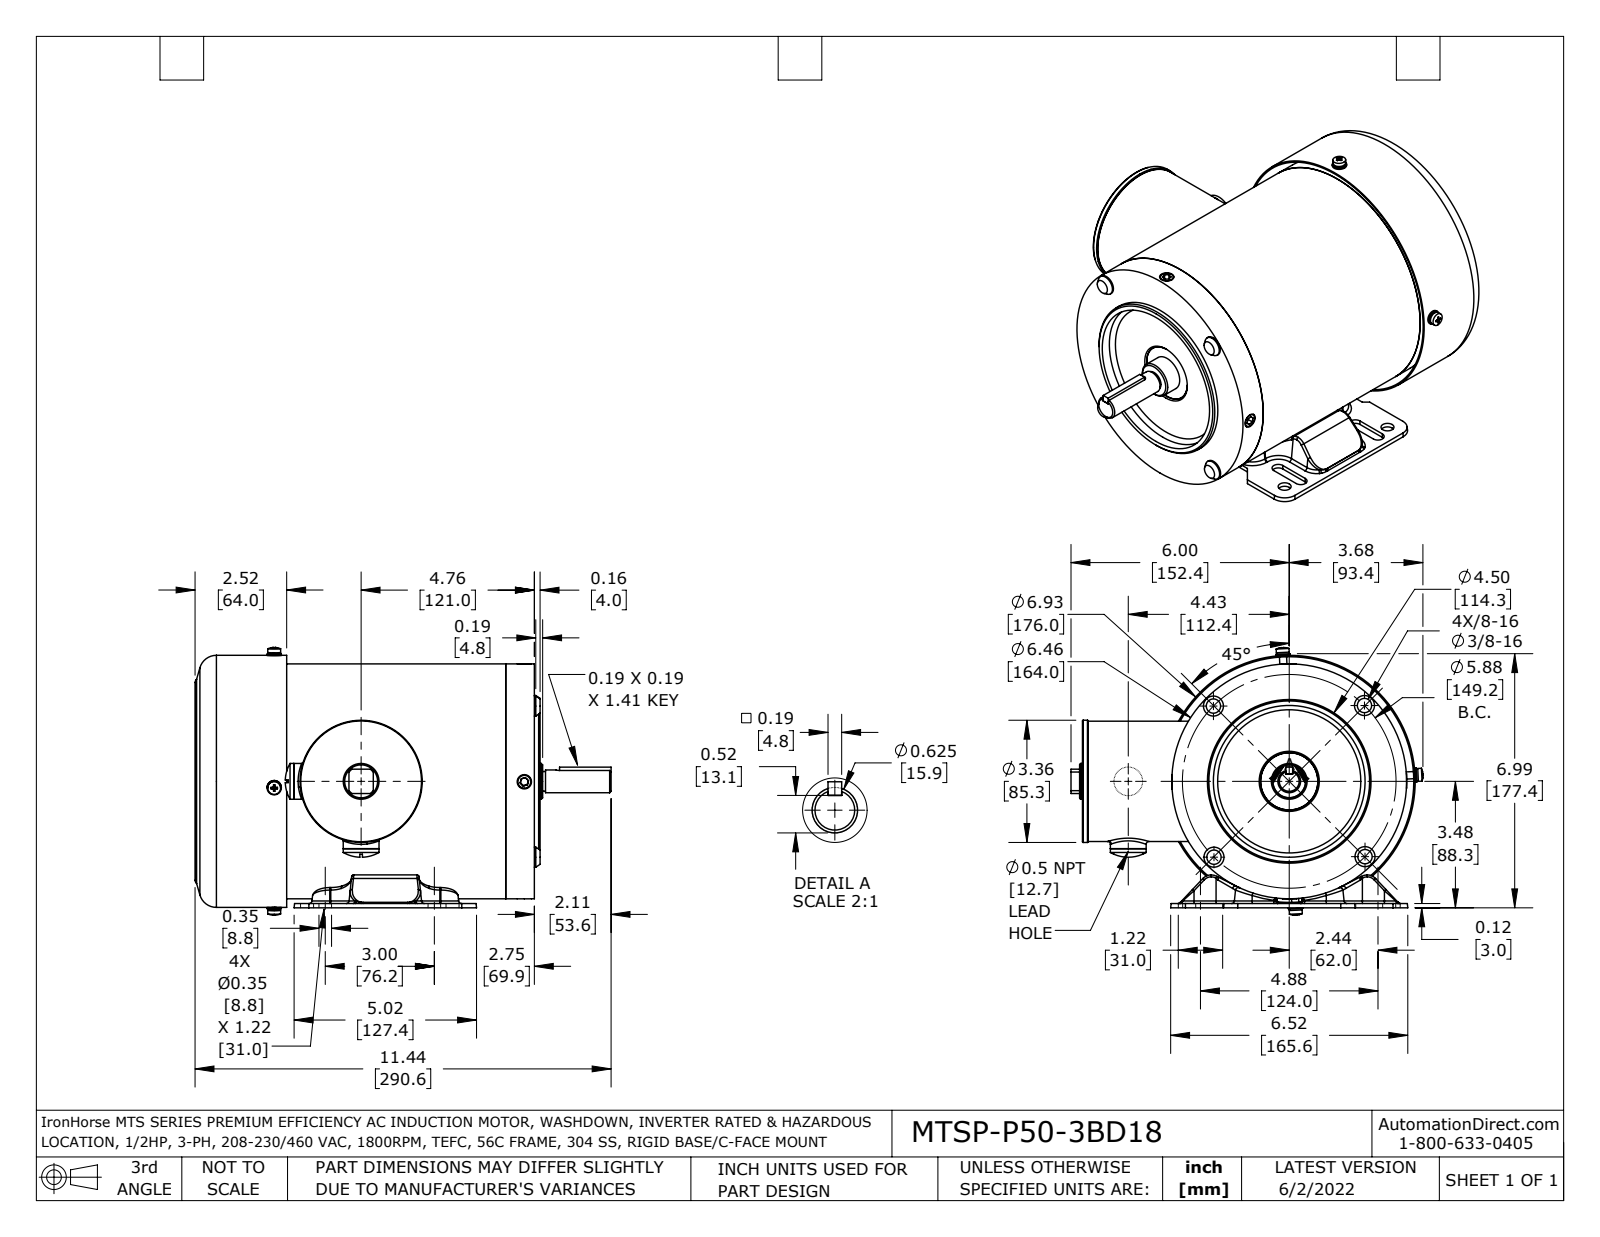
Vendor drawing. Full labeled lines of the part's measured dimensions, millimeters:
Part name (STEP PRODUCT): MTSP-P50-3BD18
STEP written by: SolidWorks 2021 (AUTOMOTIVE_DESIGN)
Units: millimetres
Bodies: 40 solids, 1660 faces (442 planar, 579 cylindrical, 639 other)
Overall size (bounding box): 290.6 × 245.9 × 186.9
Volume: 891 100 mm³ · Surface area: 601 300 mm²
Round holes (diameter × count): ⌀4.2 ×10, ⌀5.5 ×8, ⌀5.4 ×4, ⌀6 ×4, ⌀6.5 ×4, ⌀8.5 ×4, ⌀9 ×4, ⌀9.1 ×4, ⌀3 ×2, ⌀12 ×2, ⌀16.7 ×2, ⌀35 ×2
Round bosses / shafts (diameter × count): ⌀10 ×8, ⌀14 ×4, ⌀9 ×4, ⌀8.4 ×4, ⌀8 ×4, ⌀5 ×4, ⌀25 ×3, ⌀20 ×2
Partial cylindrical surfaces — rounded edges, fillets, slot ends (radius × count): R2 ×58, R1 ×39, R3.3 ×36, R0.3 ×16, R3 ×14, R4.4 ×8, R6 ×8, R1.5 ×6
Main face-to-face distances: 3, 186, 6, 1, 180, 183, 189, 49.5, 46.5, 235.5
Hole centre spacings: 74.6, 105.5, 3.4, 30, 33.3, 48.7, 76, 80.3
